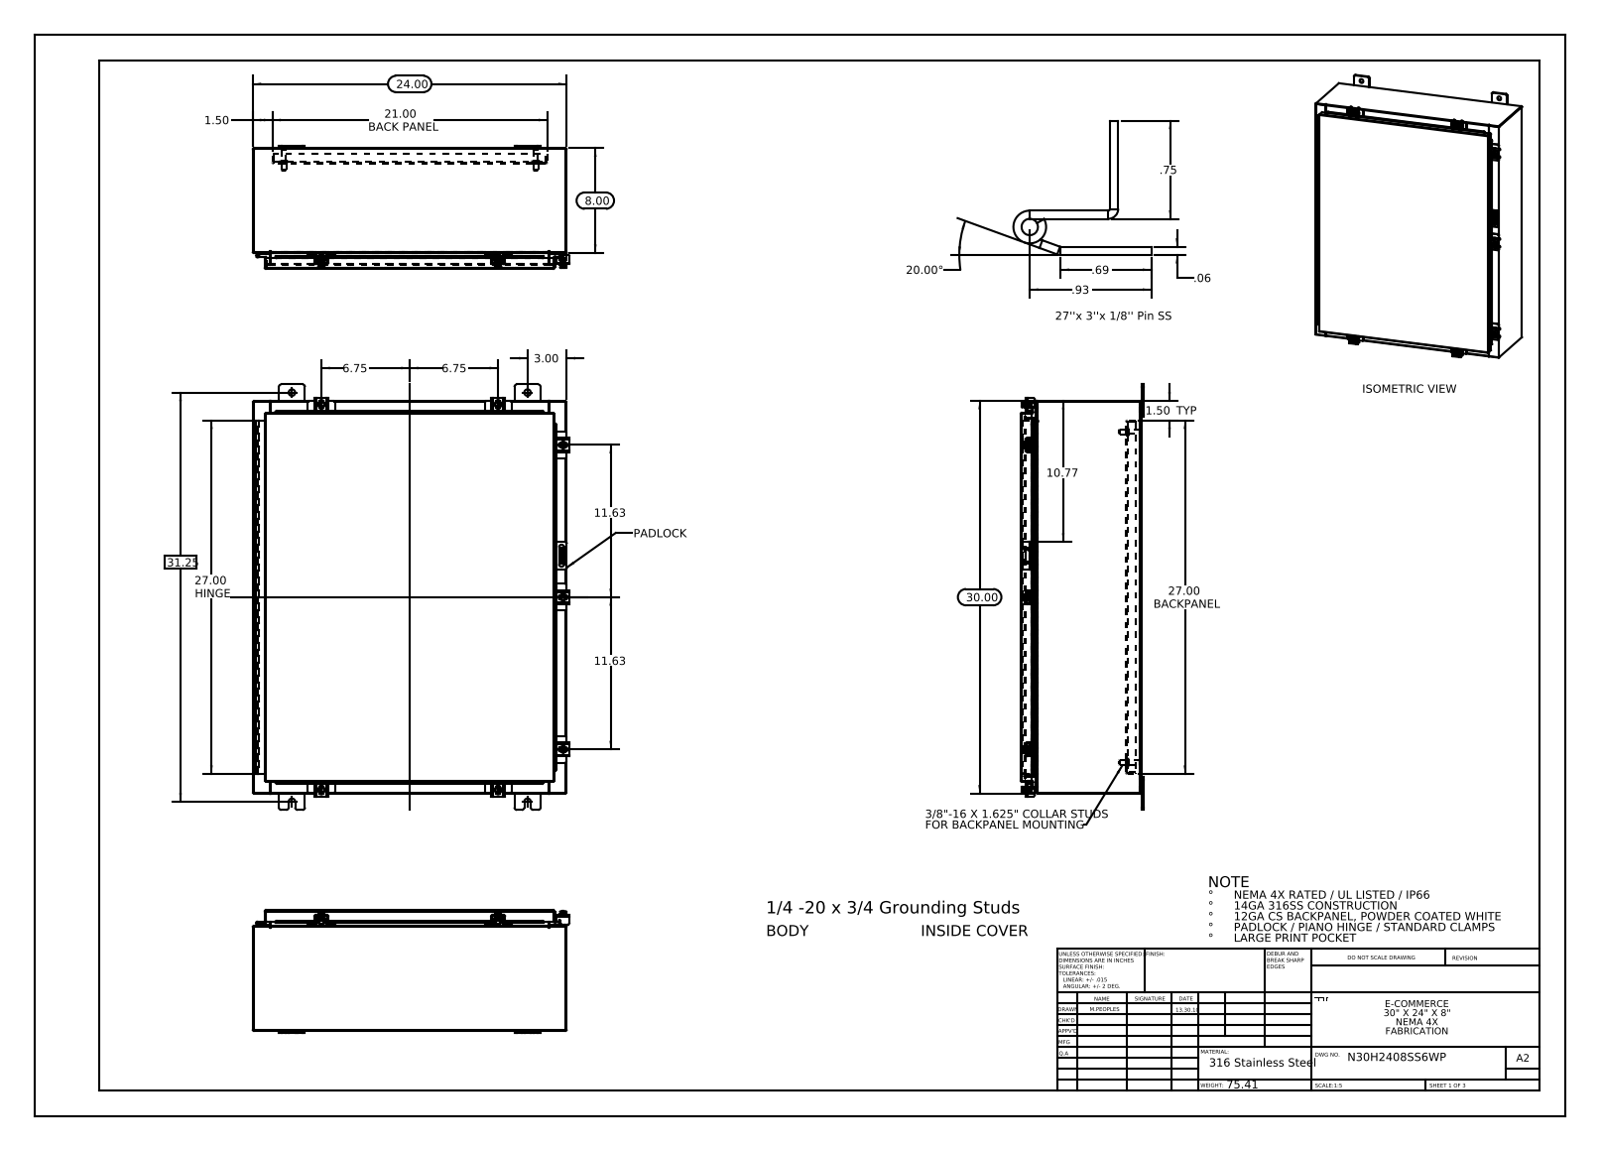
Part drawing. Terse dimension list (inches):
name: N30H2408SS6WP Top; N30H2408SS6WP Hinge Enclosure Side2; N30H2408SS6WP Clamp Assembly; N30H2408SS6WP Mounting Studs (+8 more)
written by: SolidWorks 2013 (CONFIG_CONTROL_DESIGN)
unit: in
bodies: 52 solids, 1990 faces (1056 planar, 830 cylindrical, 104 other)
size: 32.5 × 24.211 × 9.389
volume: 264.8 in³; area: 6 618 in²
holes: 8× ⌀0.5, 7× ⌀0.213, 7× ⌀0.26, 2× ⌀0.125, 1× ⌀0.125
bosses: 8× ⌀0.25, 7× ⌀0.5, 7× ⌀0.399, 4× ⌀0.625, 4× ⌀0.375, 4× ⌀0.33
rounds: 34× R0.06, 27× R0.013, 24× R0.19, 21× R0.088, 14× R0.12, 14× R0.141, 11× R0.05, 10× R0.08
face distances: 0.075, 9.126, 9.201, 9.051, 0.104, 1, 1.075, 8.051, 8.126, 1.179
hole spacings: 27.501, 31.878, 1.858, 2.277, 2.326, 2.423, 3.561, 3.561
